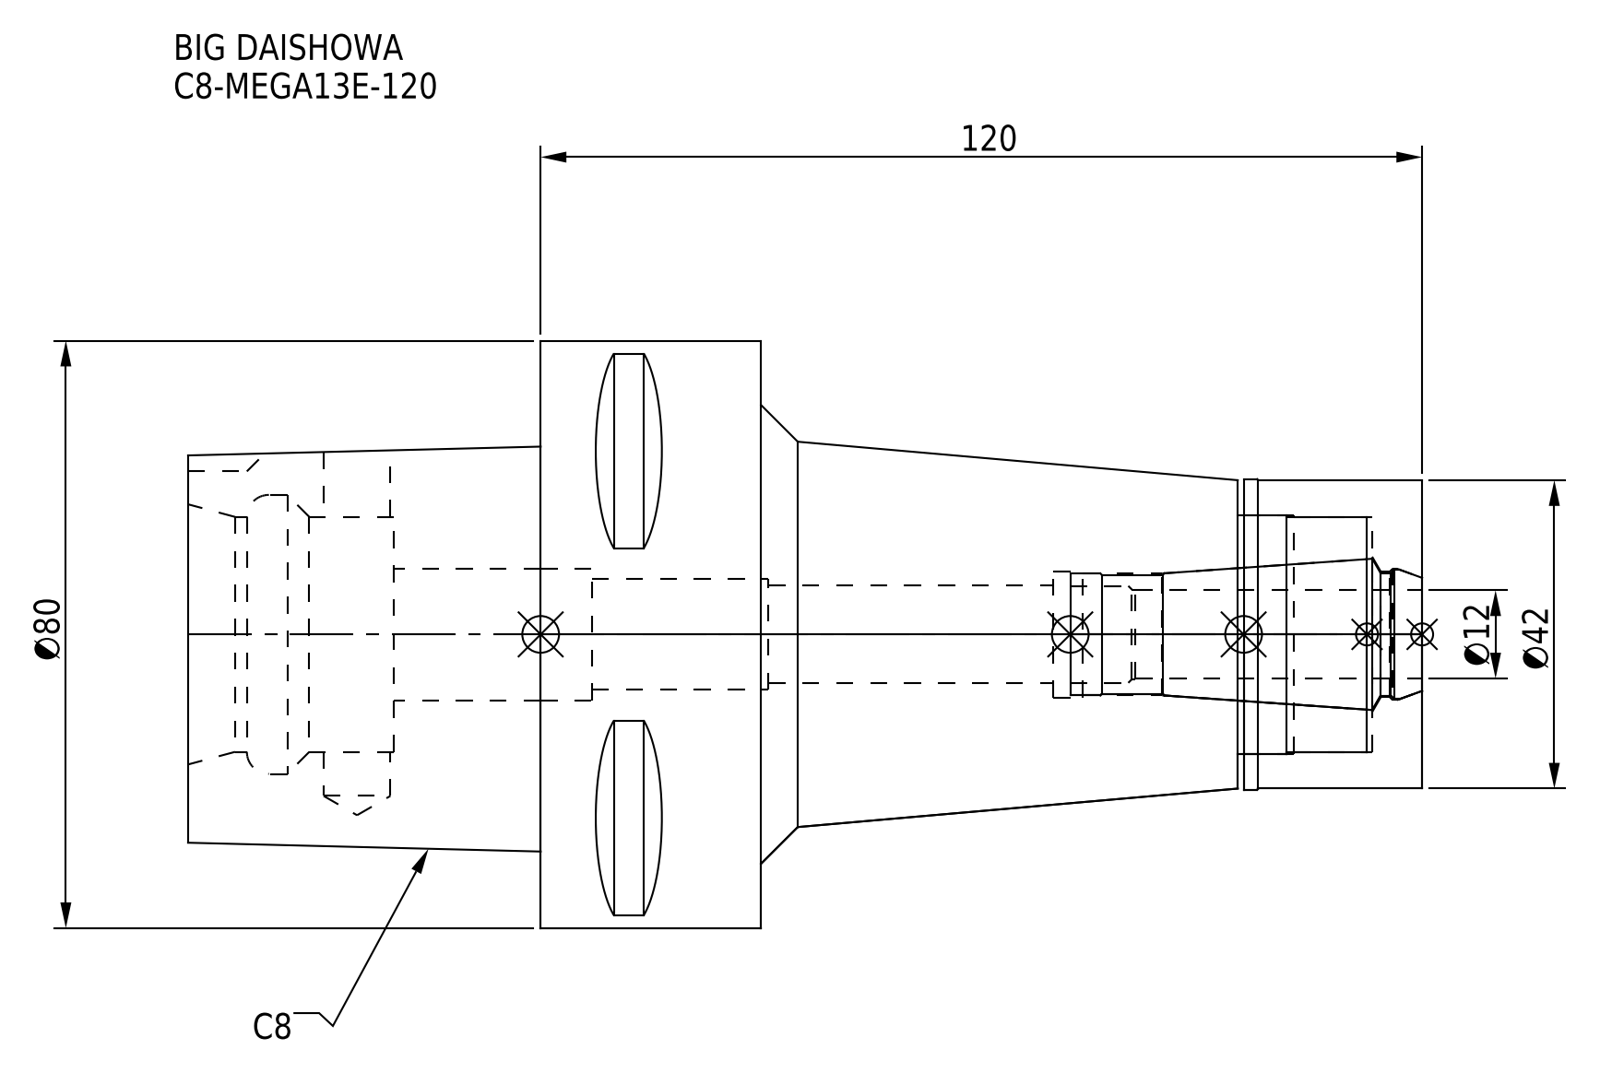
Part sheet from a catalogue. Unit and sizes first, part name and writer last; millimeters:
Units: millimetres
Overall size (bounding box): 168 × 80 × 80
Round holes (diameter × count): ⌀9.1 ×1, ⌀13.3 ×1, ⌀15 ×1, ⌀16.6 ×1, ⌀17 ×1, ⌀17.2 ×1, ⌀17.9 ×1, ⌀18 ×1, ⌀32 ×1, ⌀32.5 ×1, ⌀38 ×1
Round bosses / shafts (diameter × count): ⌀80 ×1, ⌀42.3 ×1, ⌀42 ×1
Partial cylindrical surfaces — rounded edges, fillets, slot ends (radius × count): R6 ×1
Main face-to-face distances: 30, 90, 120, 168, 78, 48, 25.1, 24.3, 65.7, 95.7
Volume: 353 306 mm³ · Surface area: 53 836 mm²
Bodies: 2 solids, 100 faces (37 planar, 39 cylindrical, 24 other)
Part name (STEP PRODUCT): C8-MEGA13E-120_1.stp; C8-MEGA13E-120; C8-MEGA13E-120-120_ASM.stp; DXF_TEMP_ASSY_ASM_4_ASM.stp (+3 more)
STEP written by: SolidWorks 2019 (CONFIG_CONTROL_DESIGN)
